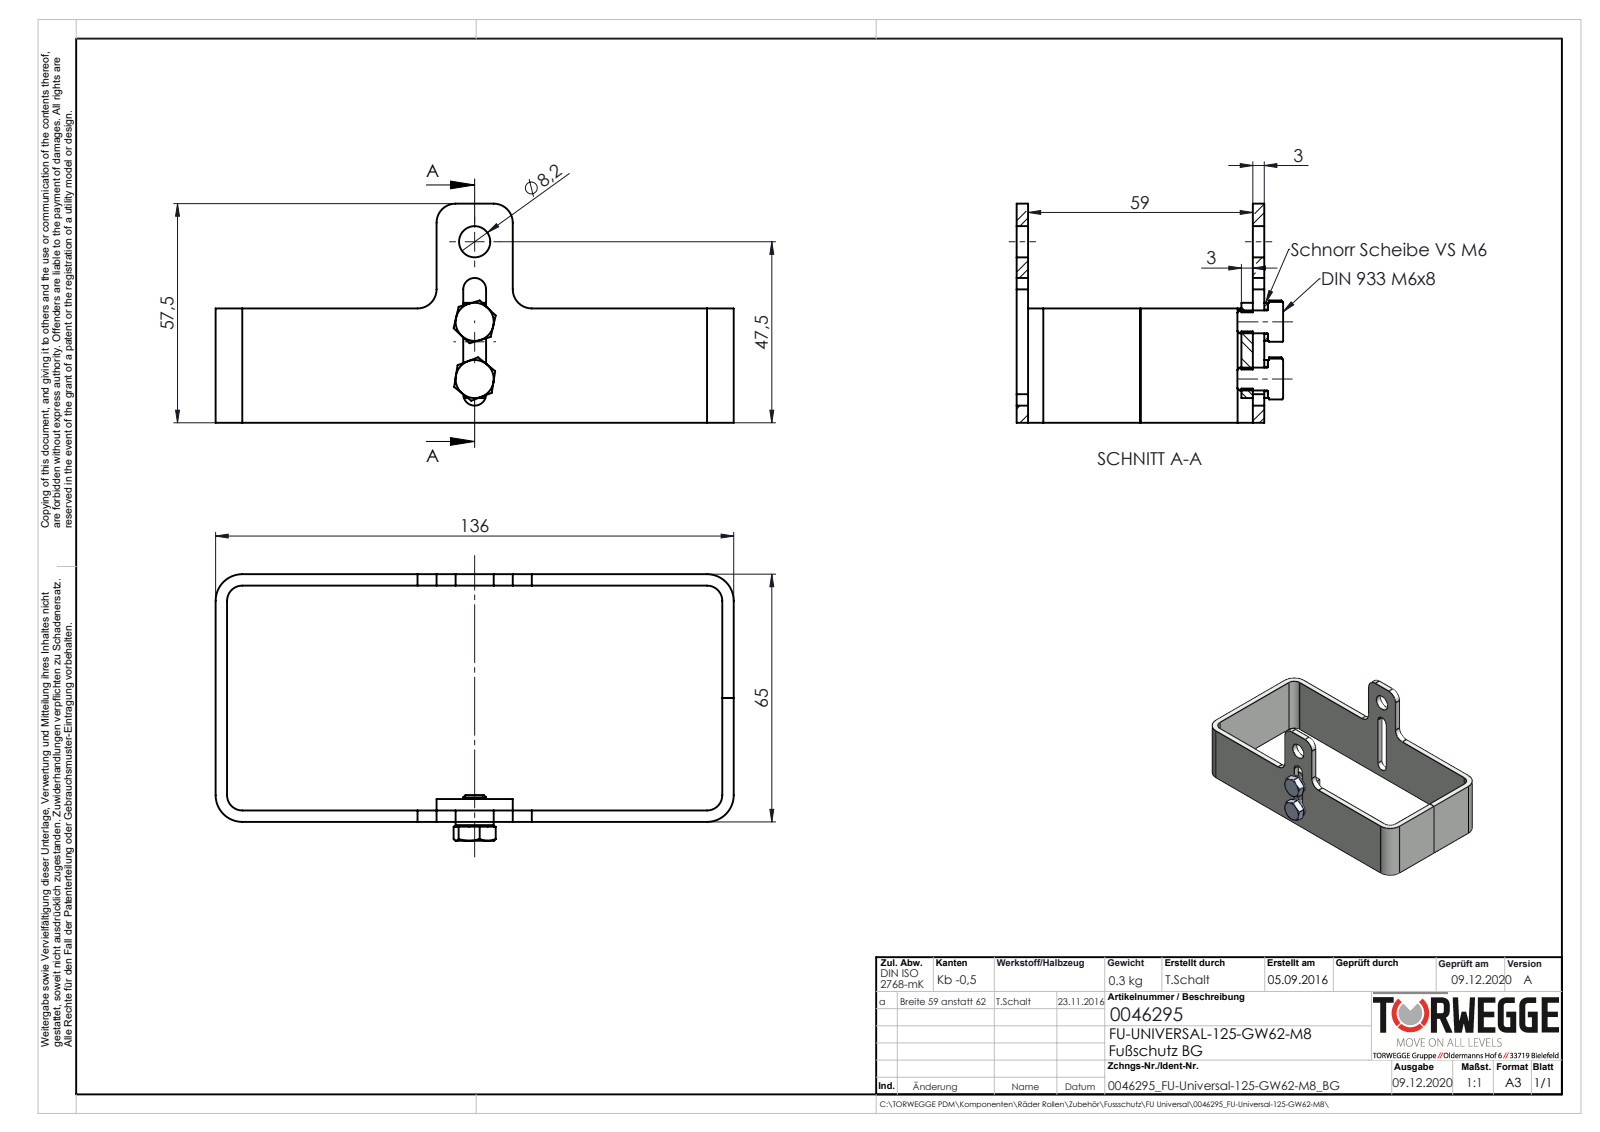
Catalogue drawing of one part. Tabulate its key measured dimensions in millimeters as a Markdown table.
| quantity | value |
| --- | --- |
| part name | 0046295 |
| STEP written by | SolidWorks 2020 (AUTOMOTIVE_DESIGN) |
| units | millimeters |
| bodies | 6 solids, 132 faces (66 planar, 44 cylindrical, 22 other) |
| overall size | 136 × 69.95 × 57.5 |
| volume | 38 674 mm³ |
| surface area | 29 853 mm² |
| round holes (diameter × count) | 5 × 2, 6.4 × 2, 8.2 × 1 |
| round bosses / shafts (diameter × count) | 10 × 2, 6 × 2 |
| partial cylindrical surfaces (radius × count) | 4 × 4, 5 × 4, 7 × 4, 3 × 2 |
| main face-to-face distances | 3, 62, 59, 65, 133, 136, 130, 30, 6, 56 |
| hole center spacings | 15, 21.02, 36.02 |
